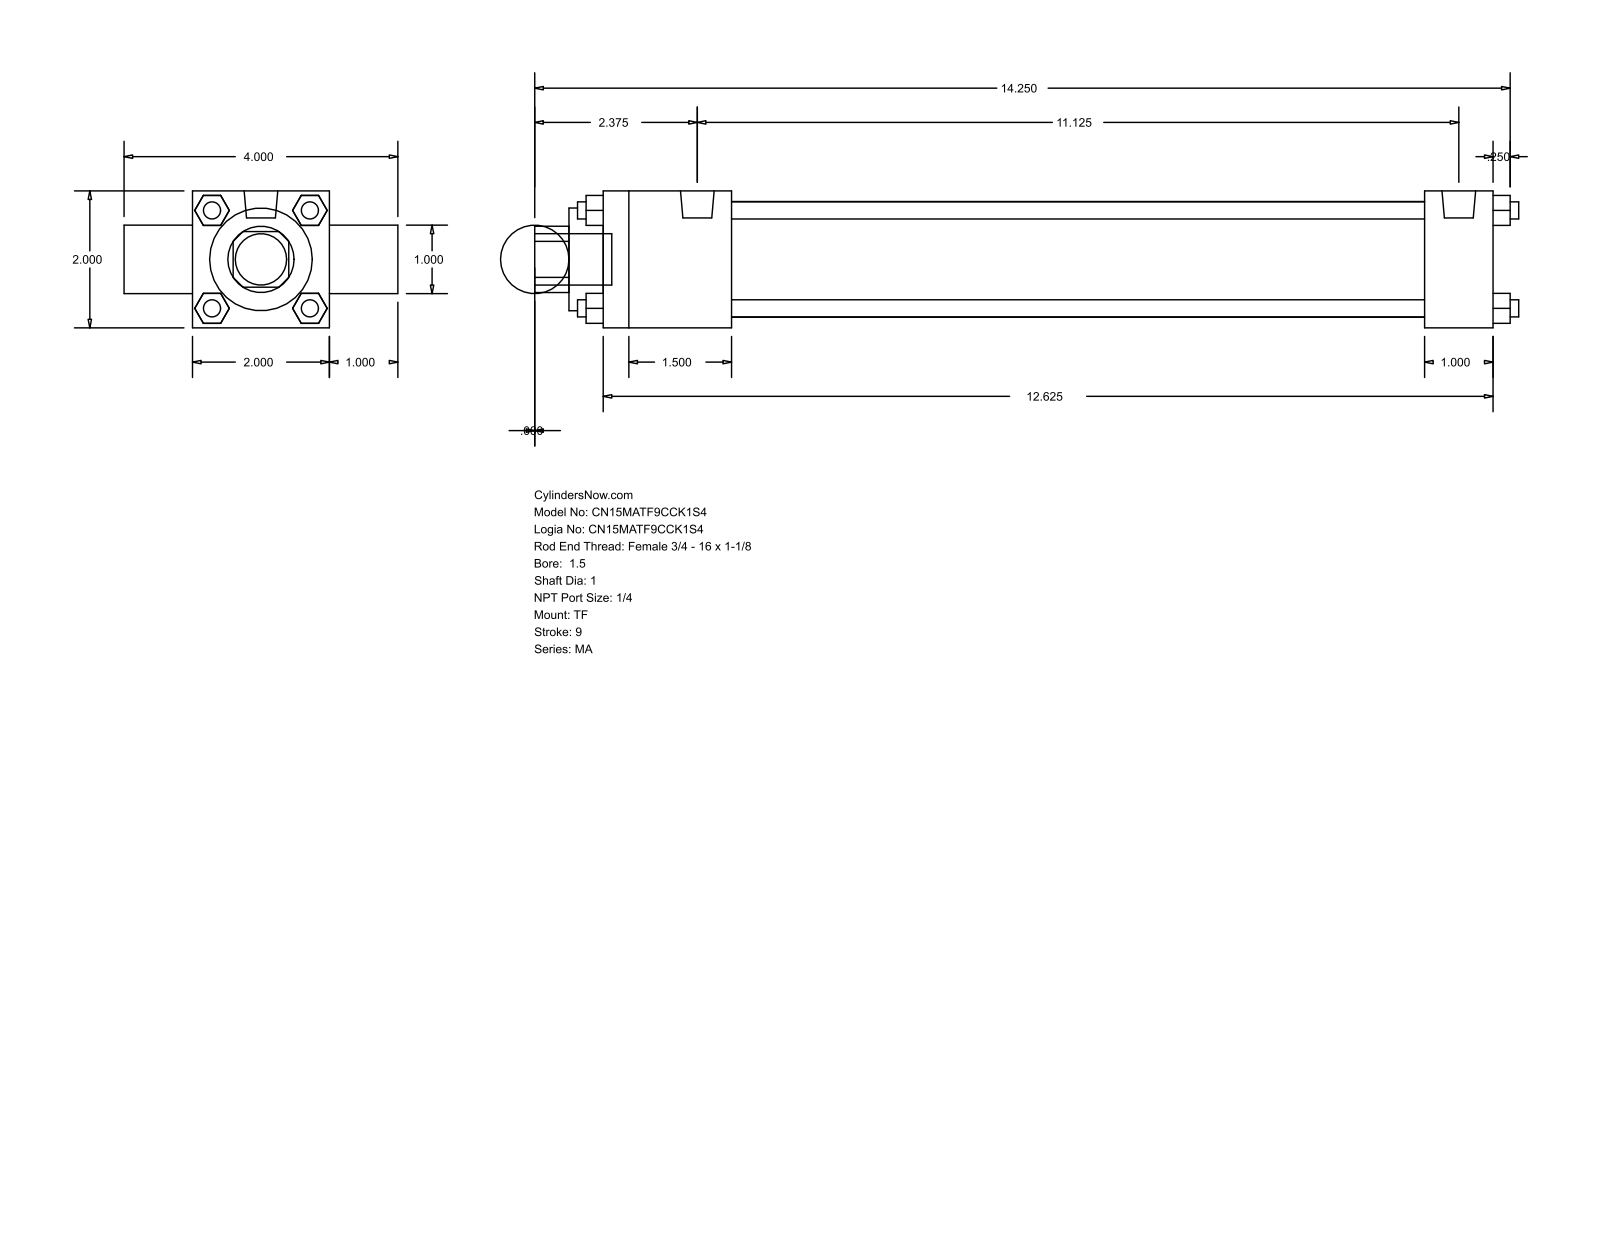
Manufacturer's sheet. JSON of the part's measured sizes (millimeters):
{"part_name": "MA_TF__0150_1", "step_written_by": "GSSL Pune (CONFIG_CONTROL_DESIGN)", "units": "millimeters", "bodies": {"solids": 0, "faces": 120, "planar": 92, "cylindrical": 28, "other": 0}, "overall_size": [365.12, 101.6, 50.8], "round_holes": [[25.4, 2], [38.1, 1], [42.93, 1]], "round_bosses_or_shafts": [[6.35, 4], [7.94, 3], [12.49, 2], [19.05, 1]], "partial_cylinders_radius": [[12.29, 1]], "face_to_face_distances": [50.8, 25.4, 330.2, 76.2, 6.35, 47.63, 304.8, 257.17, 282.57, 342.9]}
